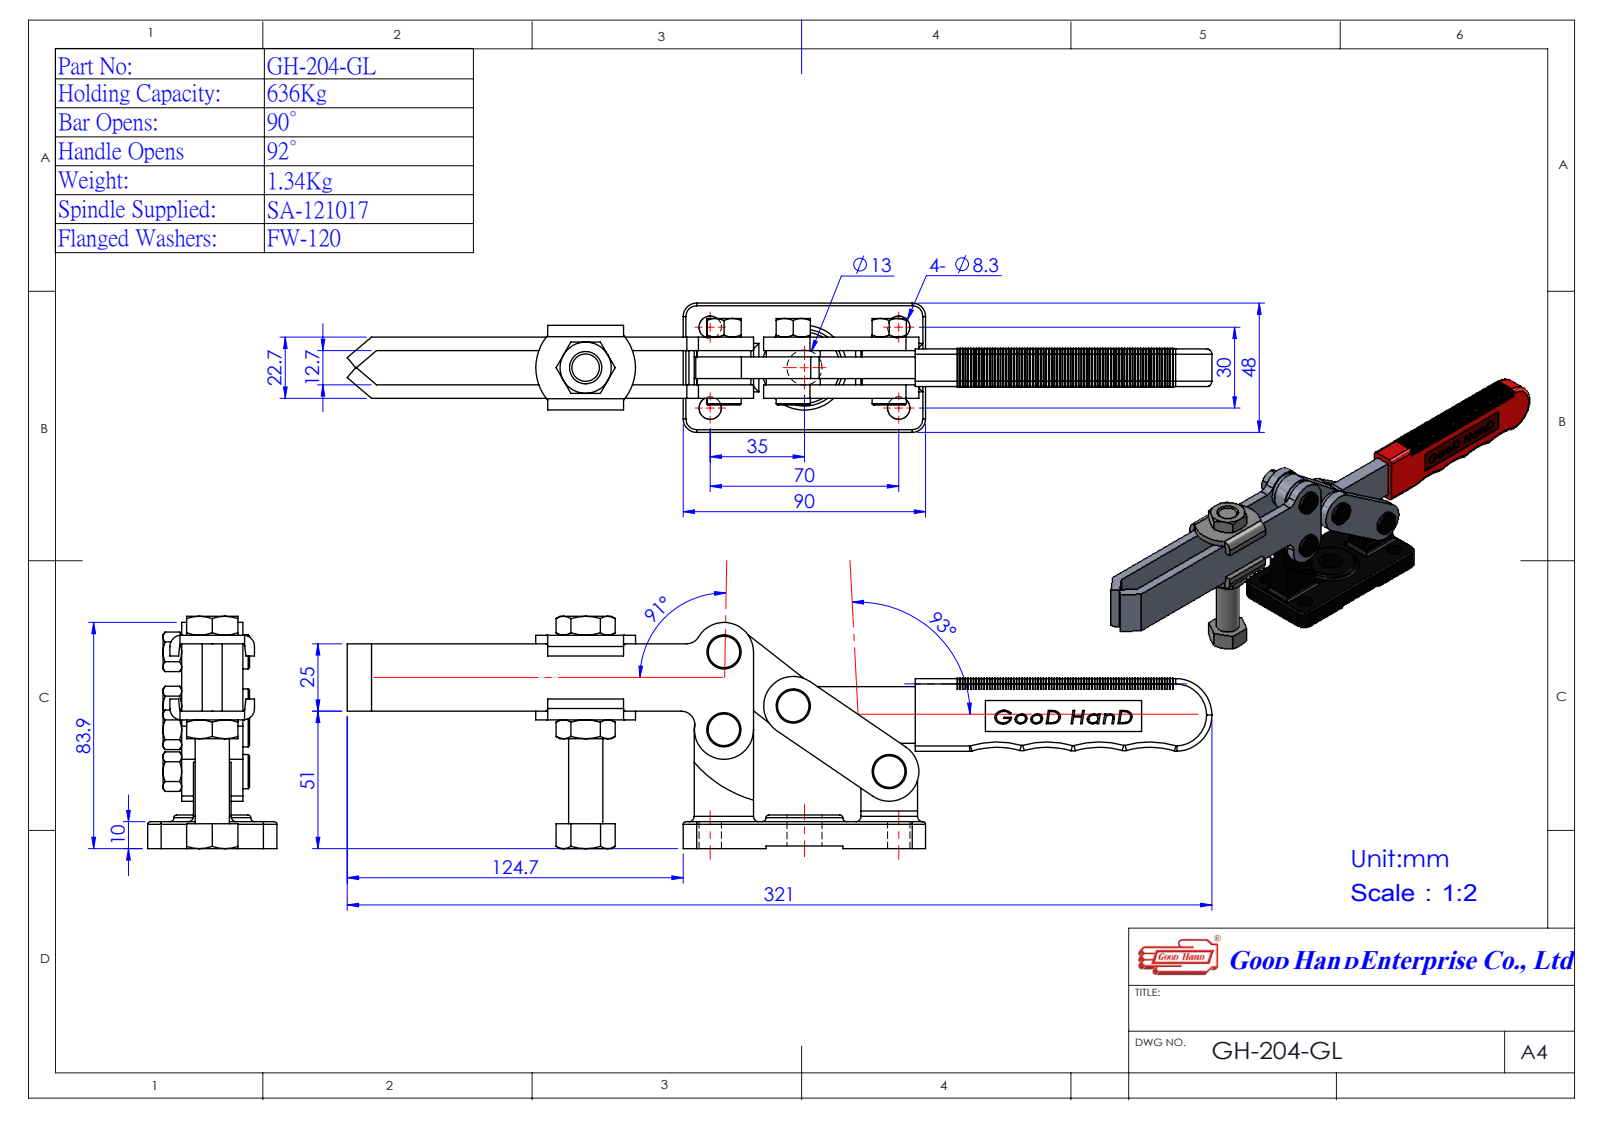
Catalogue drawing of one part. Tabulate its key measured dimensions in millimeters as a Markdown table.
| quantity | value |
| --- | --- |
| part name | GH-204-GL(簡化)-1; Group5^GH-204-GL(簡化)-1; Group1^GH-204-GL(簡化); Group2^GH-204-GL(簡化)-1 (+2 more) |
| STEP written by | SolidWorks 2016 (AUTOMOTIVE_DESIGN) |
| units | millimeters |
| bodies | 4 solids, 365 faces (151 planar, 120 cylindrical, 94 other) |
| overall size | 321 × 109.25 × 48 |
| volume | 175 027 mm³ |
| surface area | 76 077 mm² |
| round holes (diameter × count) | 8 × 4, 8.3 × 4, 13 × 1 |
| round bosses / shafts (diameter × count) | 12.7 × 5, 20 × 4, 28.5 × 1 |
| partial cylindrical surfaces (radius × count) | 5 × 8, 2 × 6, 3 × 5, 1 × 4, 4.2 × 4, 32 × 4, 11 × 3, 10.5 × 2 |
| main face-to-face distances | 5, 17.7, 7.35, 15.35, 2.35, 10.35, 3, 4.35, 18.35, 0.65 |
| hole center spacings | 38.08, 30, 70, 76.16, 27.24, 28.9, 32.63, 43.14 |
